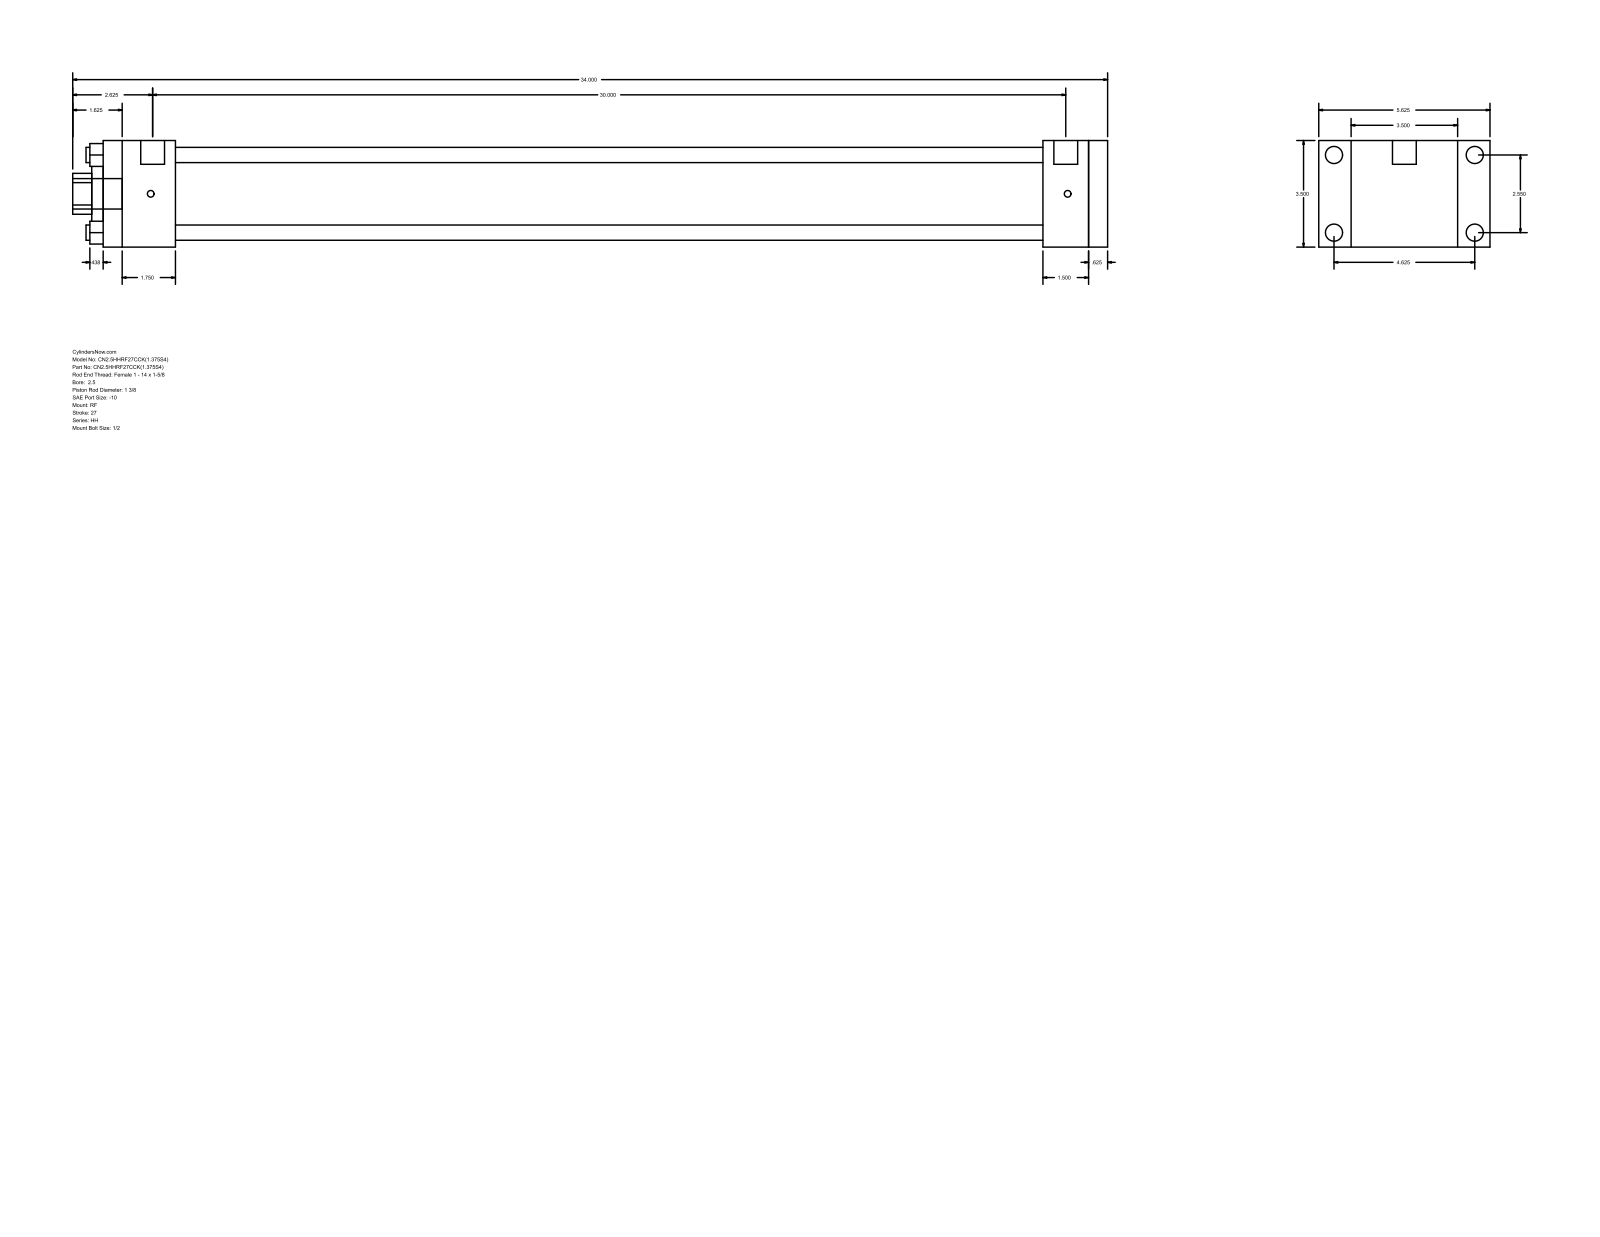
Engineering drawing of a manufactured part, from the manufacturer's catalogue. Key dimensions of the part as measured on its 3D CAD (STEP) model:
Part name (STEP PRODUCT): HH_RF__0250_1.375
STEP written by: GSSL Pune (CONFIG_CONTROL_DESIGN)
Units: millimetres
Bodies: 0 solids, 92 faces (64 planar, 28 cylindrical, 0 other)
Overall size (bounding box): 863.6 × 142.88 × 88.9
Round holes (diameter × count): ⌀12.7 ×4, ⌀34.92 ×1, ⌀50.8 ×1, ⌀73.03 ×1
Round bosses / shafts (diameter × count): ⌀14.3 ×4, ⌀5.56 ×4, ⌀19.84 ×2, ⌀25.4 ×1
Partial cylindrical surfaces — rounded edges, fillets, slot ends (radius × count): R17.06 ×1
Main face-to-face distances: 88.9, 15.87, 822.33, 838.2, 60.32, 762.01, 777.88, 784.22, 723.9, 38.11
Hole centre spacings: 45.79, 64.76, 91.58
